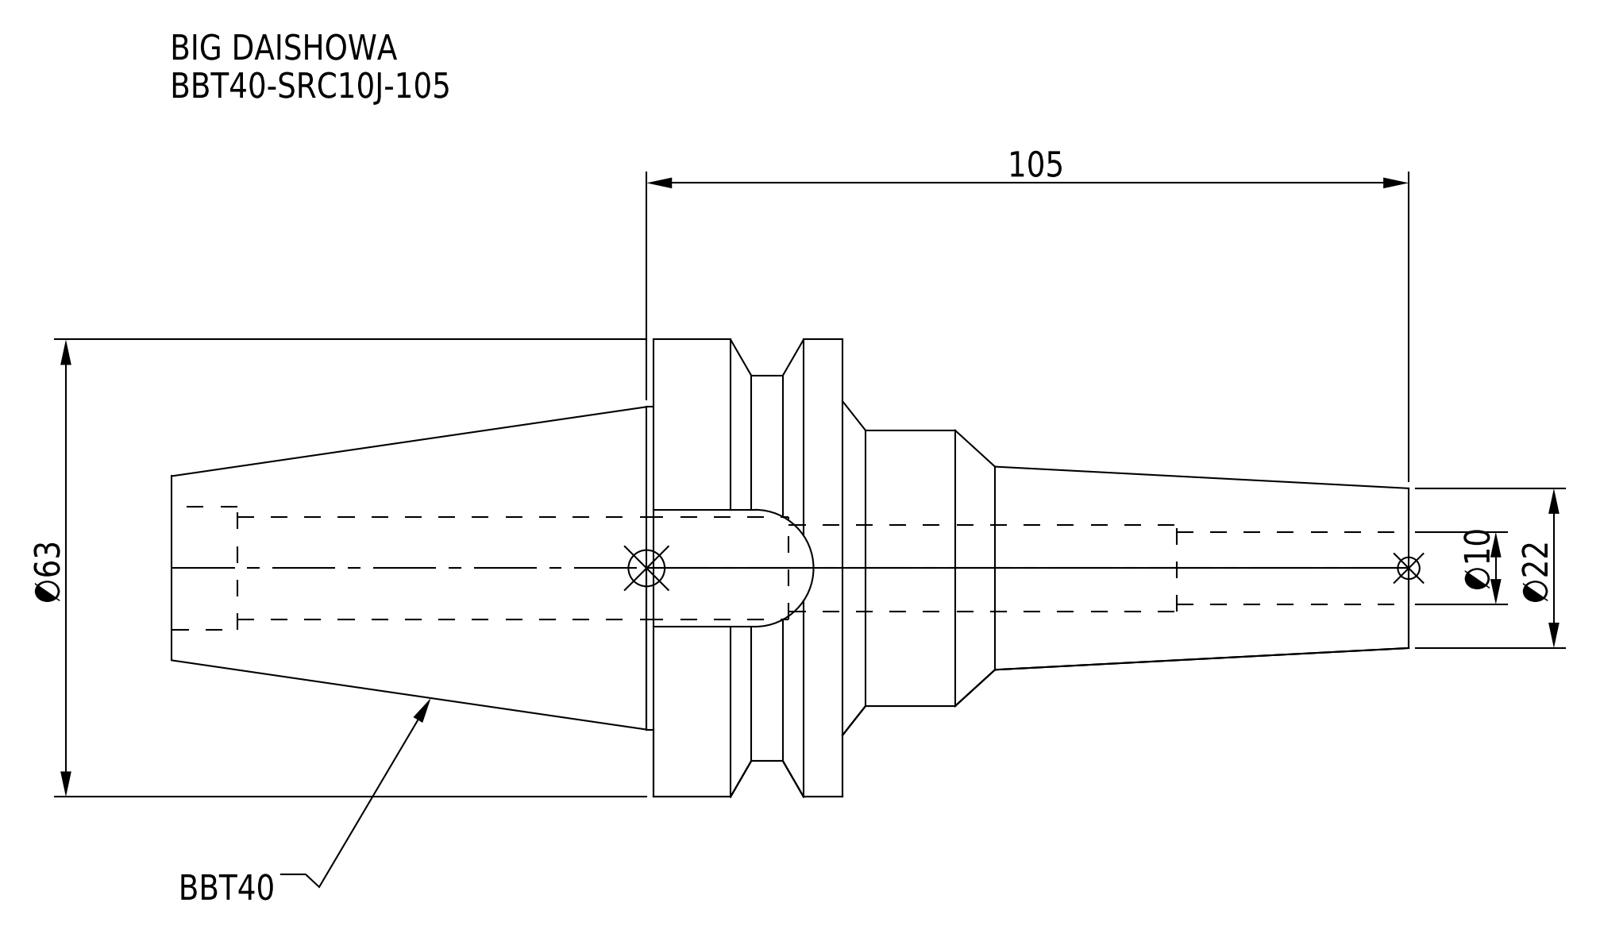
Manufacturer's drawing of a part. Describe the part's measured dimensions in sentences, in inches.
The part is named "BBT40-SRC10J-105". Its 3-D file was written by "CREO PARAMETRIC BY PTC INC, 2016380 (AUTOMOTIVE_DESIGN)". It is 1 solid with 47 faces: 13 planar, 22 cylindrical and 12 other. Overall it measures 6.709 by 2.48 by 2.48 inches. Its volume is 10.02 cubic inches and its surface area 49.07 square inches. Round holes: 1 of diameter 0.394, 1 of diameter 0.472, 1 of diameter 0.559, 1 of diameter 0.669. Round bosses or shafts: 1 of diameter 2.48, 1 of diameter 2.087, 1 of diameter 1.75, 1 of diameter 1.496. Partial cylindrical surfaces (rounded edges, fillets, slot ends): 1 of radius 0.317. The main face-to-face distances are 1.024, 1.772, 3.071, 4.094, 6.709, 3.638, 2.614, 0.634, 6.354, 3.283.
